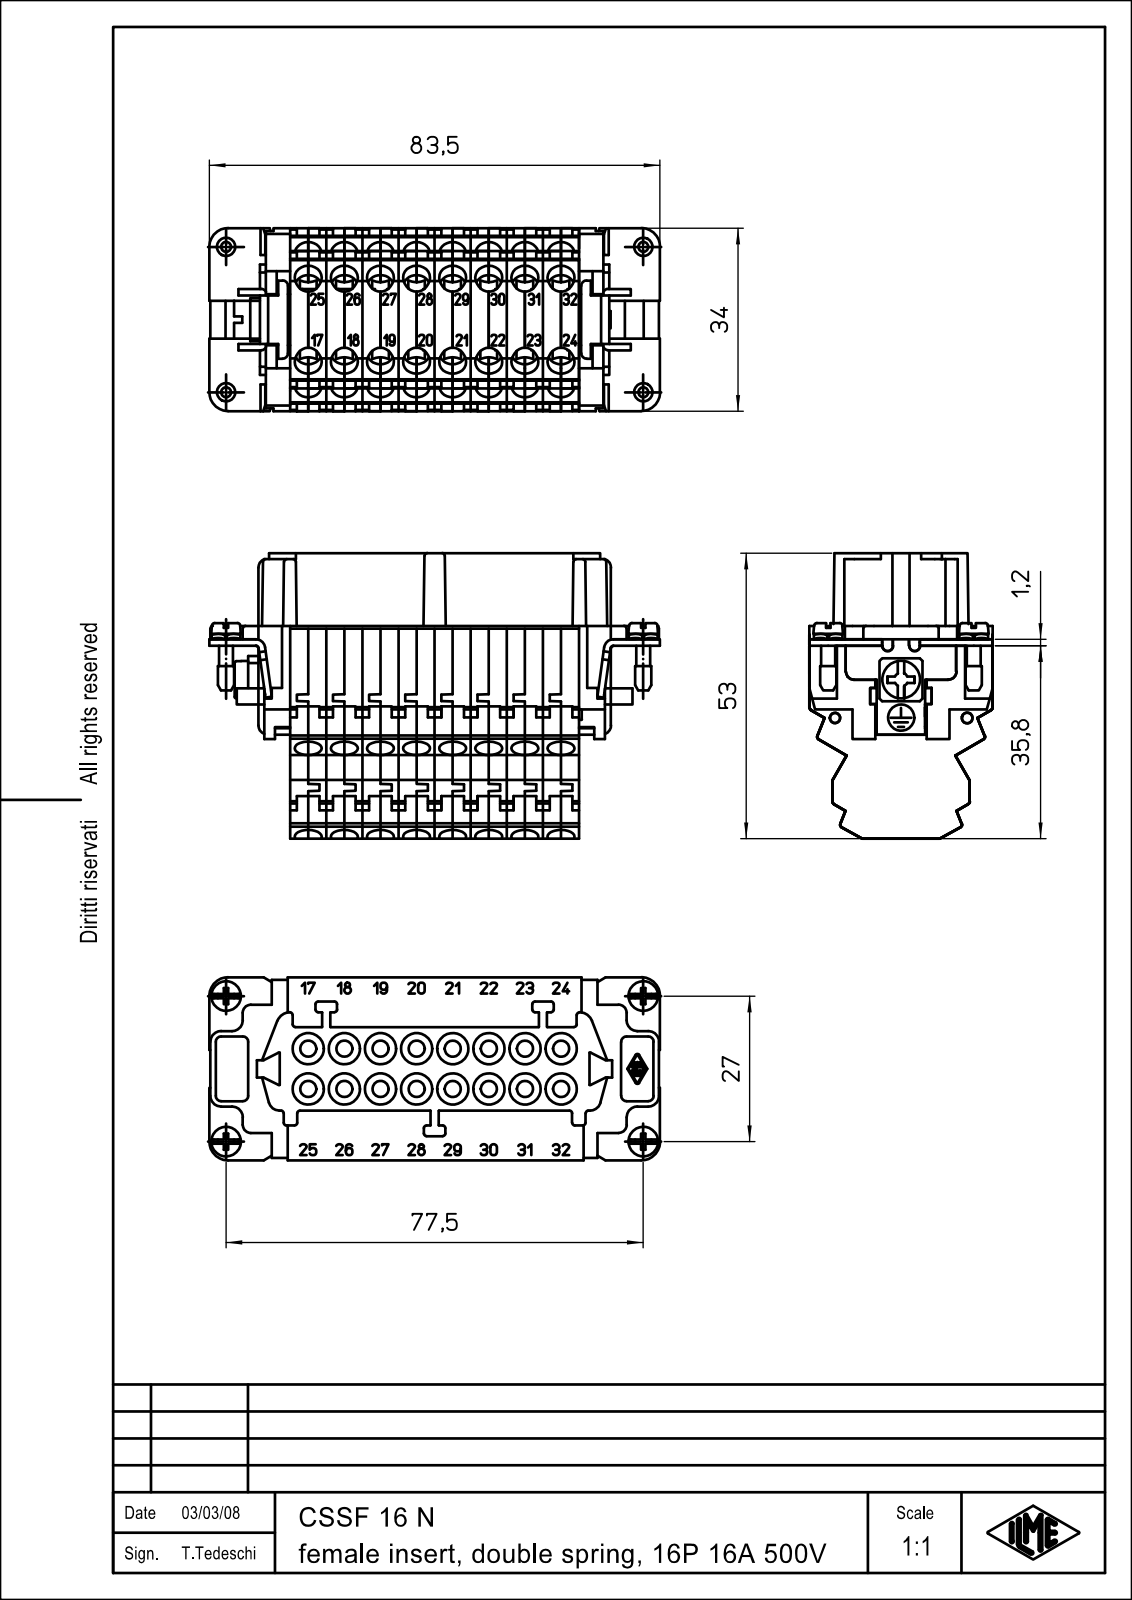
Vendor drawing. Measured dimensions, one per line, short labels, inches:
name: CSSF_16_N
written by: PTC Creo Elements/Direct Modeling 19.0B 21-Mar-2015 (C) Parametric Technology GmbH (AUTOMOTIVE_DESIGN)
unit: in
bodies: 1 solid, 1817 faces (1191 planar, 464 cylindrical, 162 other)
size: 3.291 × 2.094 × 1.339
volume: 4.29 in³; area: 66.07 in²
holes: 32× ⌀0.197, 20× ⌀0.11, 16× ⌀0.228, 1× ⌀0.102, 1× ⌀0.165
bosses: 4× ⌀0.217, 4× ⌀0.118, 4× ⌀0.102, 1× ⌀0.276, 1× ⌀0.22, 1× ⌀0.157
rounds: 59× R0.02, 22× R0.039, 10× R0.059, 10× R0.079, 6× R0.012, 6× R0.047, 4× R0.035, 4× R0.138
face distances: 0.264, 0.528, 0.791, 1.055, 0.263, 0.527, 0.791, 1.319, 0.265, 1.054
hole spacings: 0.264, 0.528, 0.791, 0.708, 1.055, 0.922, 1.319, 0.396
